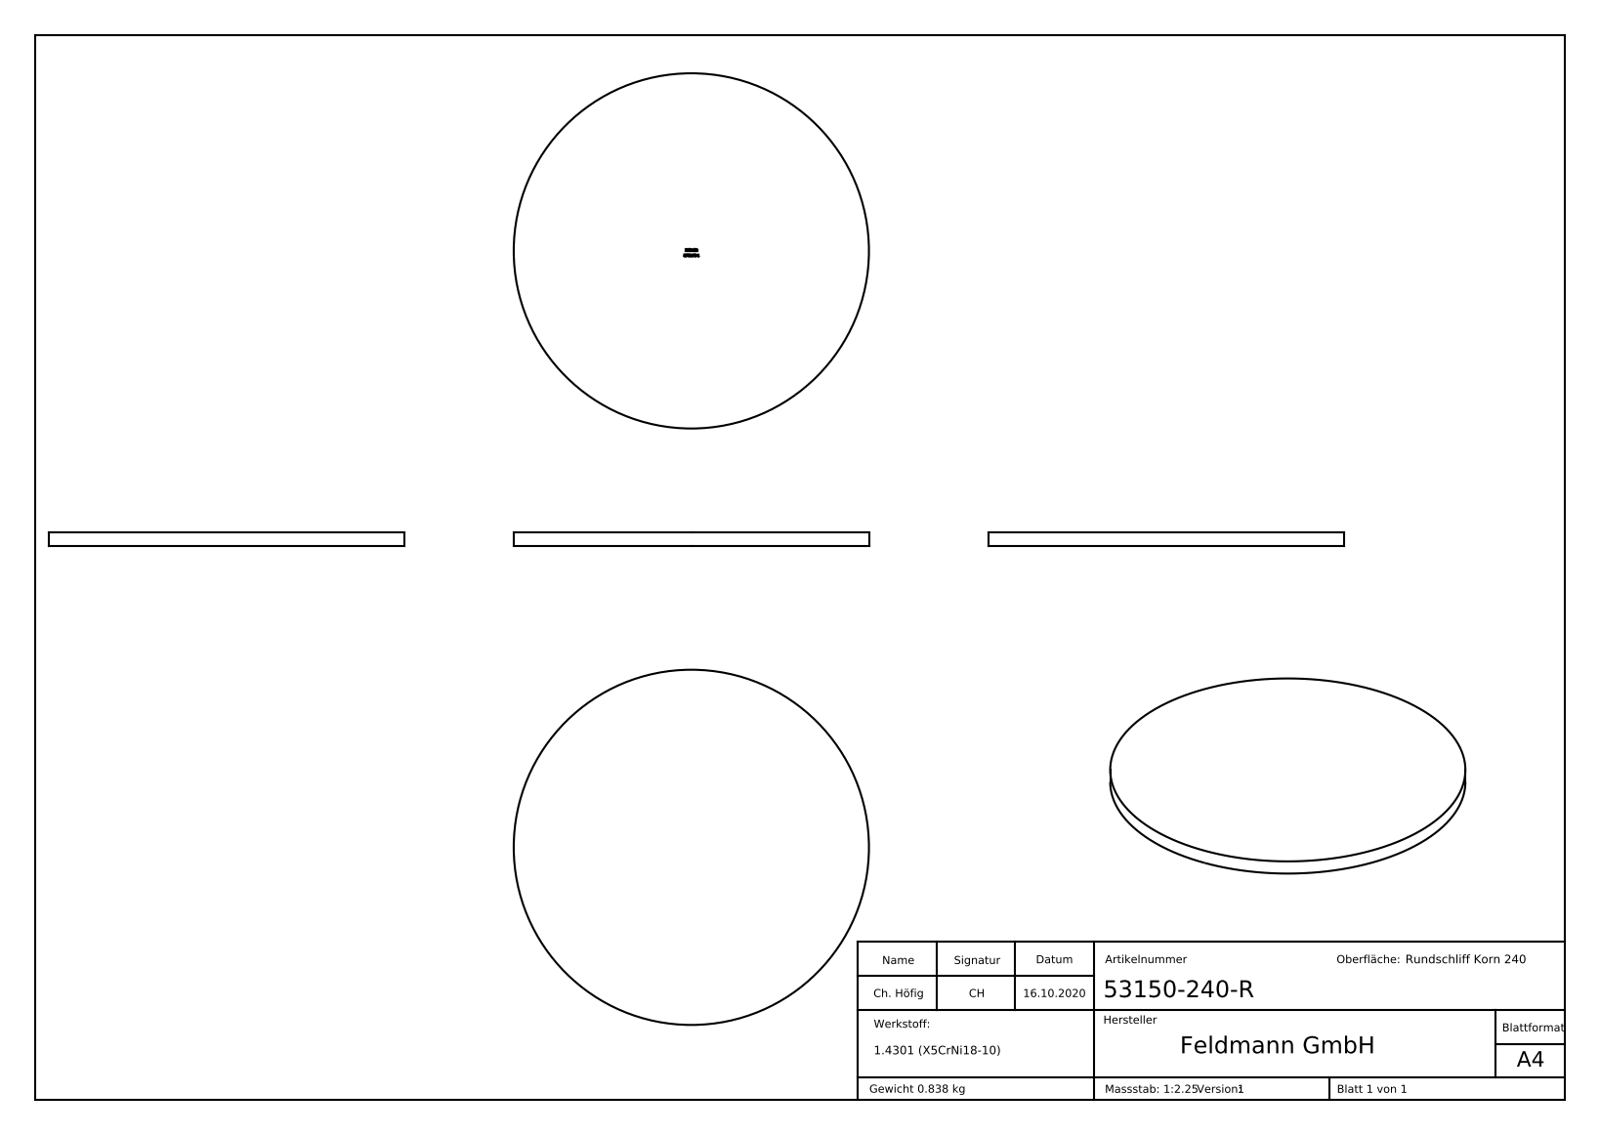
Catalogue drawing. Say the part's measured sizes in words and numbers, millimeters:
The part is named "53150-240-R". Its 3-D file was written by "SolidWorks 2018 (CONFIG_CONTROL_DESIGN)". It is 1 solid with 250 faces: 141 planar, 2 cylindrical and 107 other. Overall it measures 150 by 150 by 6 millimeters. Its volume is 106 029 cubic millimeters and its surface area 38 177 square millimeters. Round bosses or shafts: 1 of diameter 150. The main face-to-face distances are 6, 5.9, 1.21, 0.79, 1.28, 0.99, 3.86, 0.92, 2.94, 1.78.
